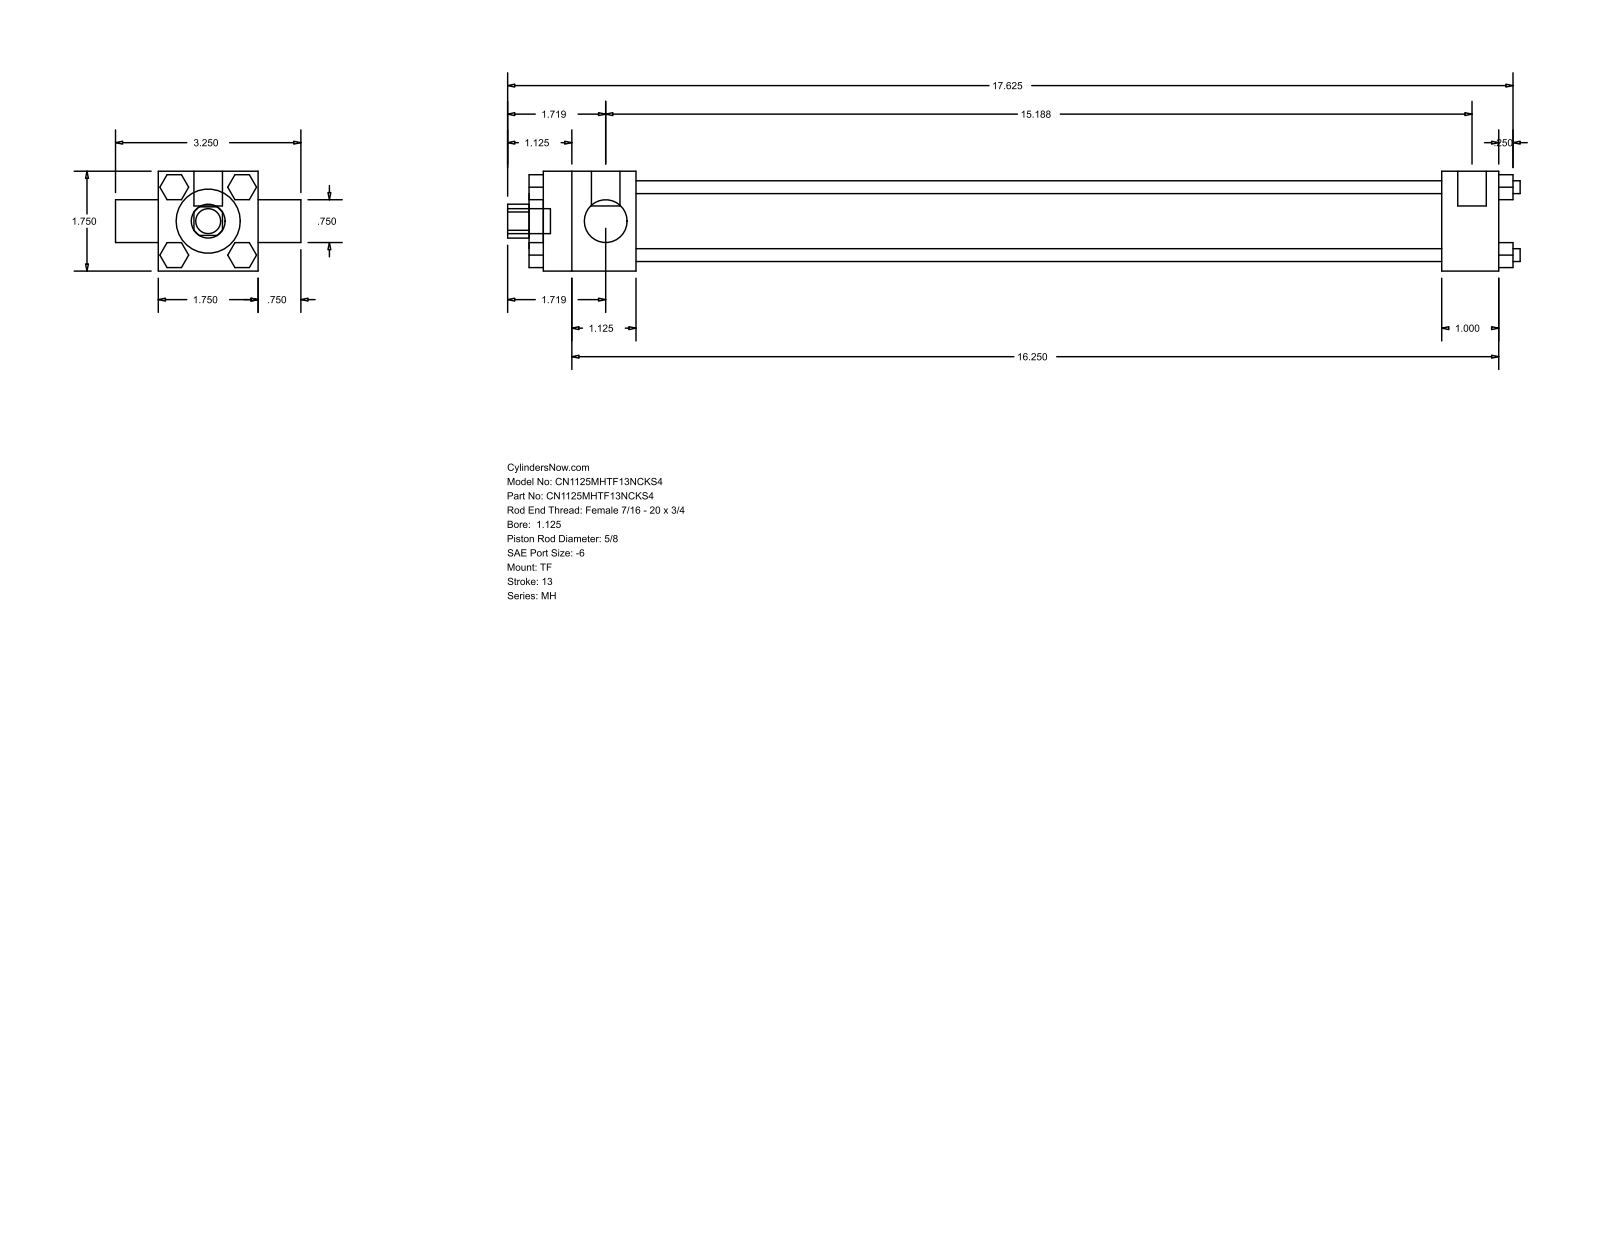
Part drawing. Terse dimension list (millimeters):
name: MH_TF__0112_0.625
written by: GSSL Pune (CONFIG_CONTROL_DESIGN)
unit: mm
bodies: 0 solids, 120 faces (92 planar, 28 cylindrical, 0 other)
size: 450.85 × 82.55 × 44.45
holes: 1× ⌀15.88, 1× ⌀19.05, 1× ⌀28.57, 1× ⌀34.92
bosses: 4× ⌀5.71, 3× ⌀5.56, 2× ⌀12.7, 1× ⌀11.11
rounds: 1× R7.54
face distances: 44.46, 11.11, 358.78, 384.17, 25.39, 41.27, 400.05, 425.44, 47.62, 6.35
